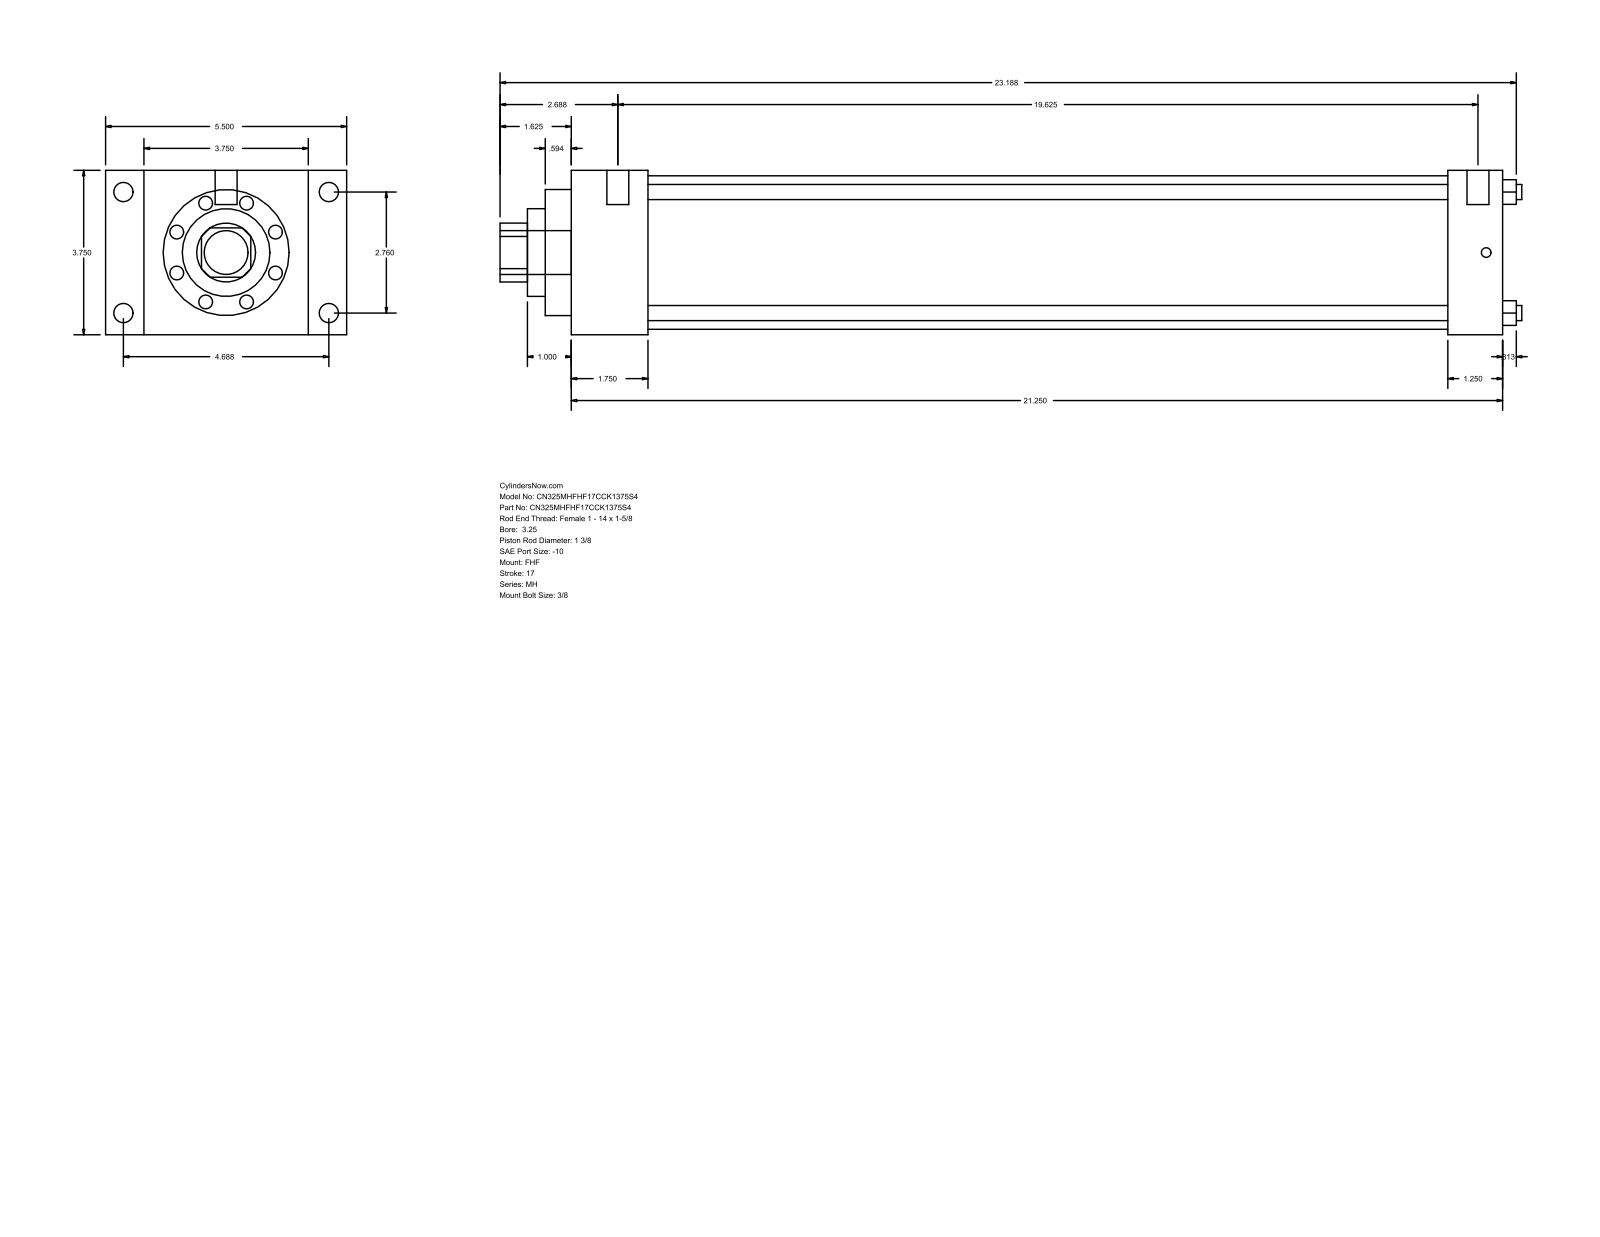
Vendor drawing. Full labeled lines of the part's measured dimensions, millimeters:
Part name (STEP PRODUCT): MH_FHF__0325_1.375
STEP written by: GSSL Pune (CONFIG_CONTROL_DESIGN)
Units: millimetres
Bodies: 0 solids, 90 faces (61 planar, 29 cylindrical, 0 other)
Overall size (bounding box): 592.14 × 139.7 × 95.25
Round holes (diameter × count): ⌀8.76 ×4, ⌀34.92 ×1, ⌀50.8 ×1, ⌀73.03 ×1, ⌀88.9 ×1
Round bosses / shafts (diameter × count): ⌀11.13 ×4, ⌀5.56 ×4, ⌀12.7 ×2, ⌀25.4 ×1
Partial cylindrical surfaces — rounded edges, fillets, slot ends (radius × count): R17.06 ×1
Main face-to-face distances: 95.24, 539.75, 44.45, 495.3, 22.23, 117.47, 139.7, 508, 463.55, 31.75
Hole centre spacings: 49.57, 70.1, 99.14
